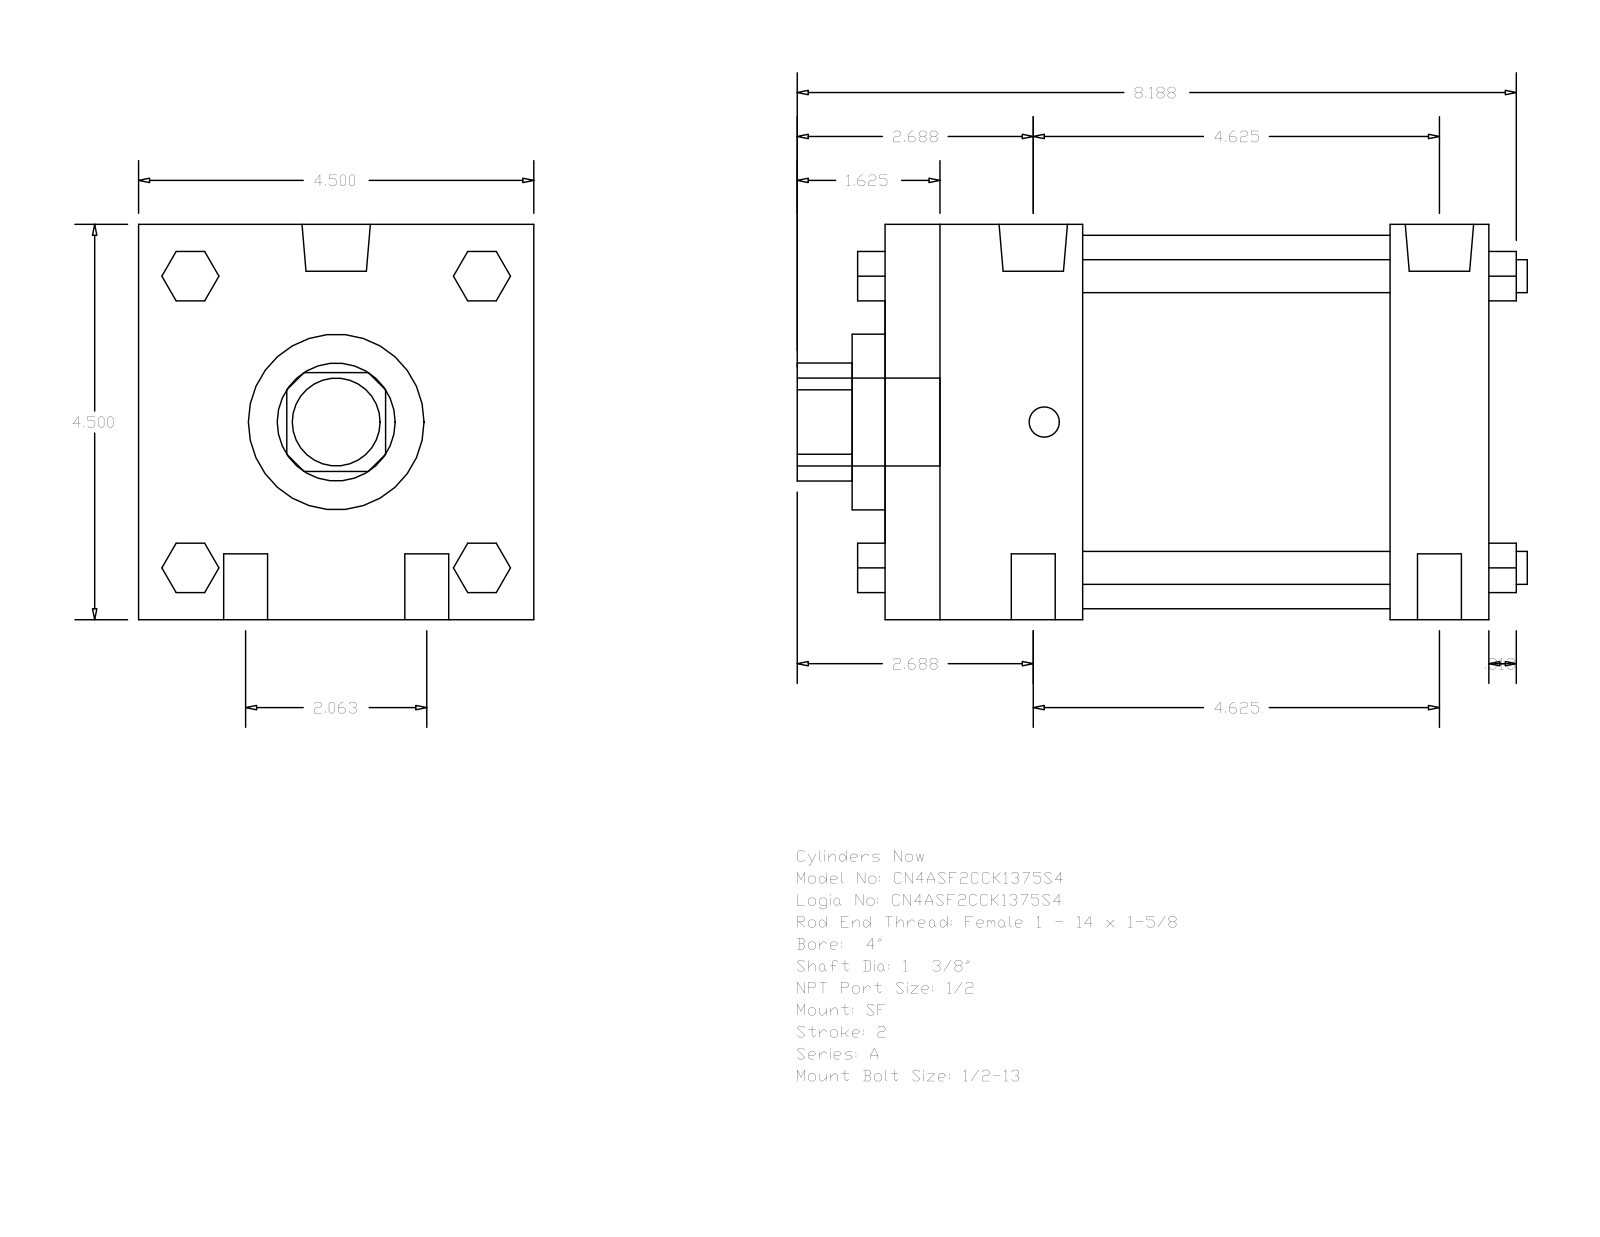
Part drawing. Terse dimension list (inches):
name: A_SF__0400_1.375
written by: GSSL Pune (CONFIG_CONTROL_DESIGN)
unit: in
bodies: 0 solids, 124 faces (94 planar, 30 cylindrical, 0 other)
size: 8.313 × 4.5 × 4.5
holes: 1× ⌀1.375, 1× ⌀2, 1× ⌀4.25
bosses: 4× ⌀0.5, 4× ⌀0.375, 2× ⌀0.778, 2× ⌀0.344, 1× ⌀1
rounds: 1× R0.672
face distances: 4.5, 6.875, 1.125, 5.75, 2.25, 3.5, 4.625, 0.563, 0.375, 2.625
